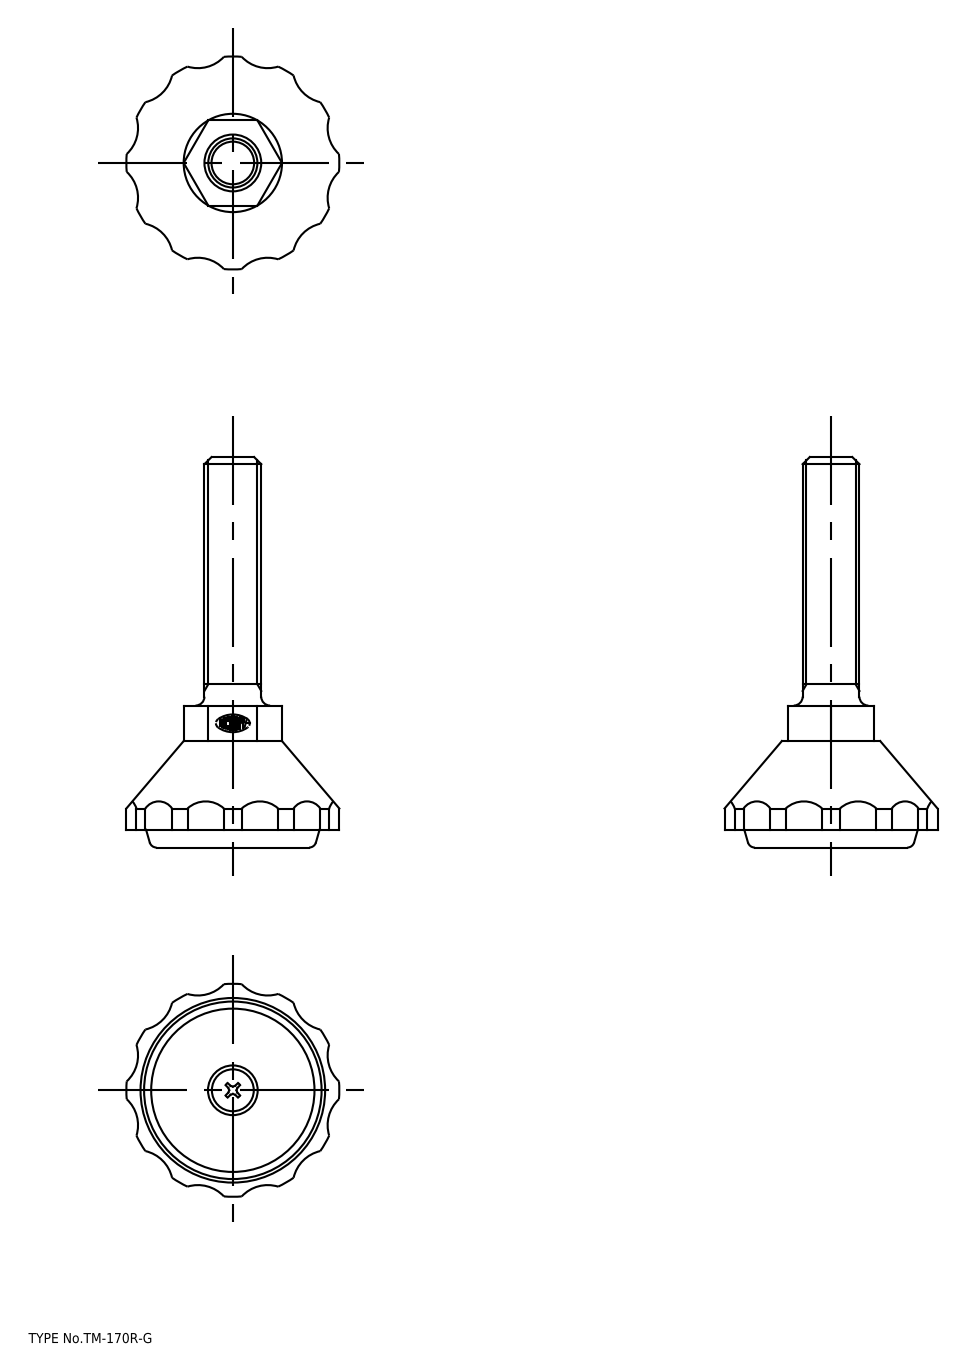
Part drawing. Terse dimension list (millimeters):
name: washer; screw; rubber pad; bolt
written by: spGate 17.5.1 (AUTOMOTIVE_DESIGN)
unit: mm
bodies: 4 solids, 108 faces (42 planar, 48 cylindrical, 18 other)
size: 110 × 60 × 60
volume: 68 155 mm³; area: 19 065 mm²
holes: 1× ⌀4.4, 1× ⌀10, 1× ⌀14, 1× ⌀52
bosses: 1× ⌀50, 1× ⌀16, 1× ⌀11.8, 1× ⌀9.5
rounds: 12× R10, 1× R2.5, 1× R30
face distances: 2, 9, 11, 4, 5, 6, 23.98, 5.7, 0.7, 3.3
